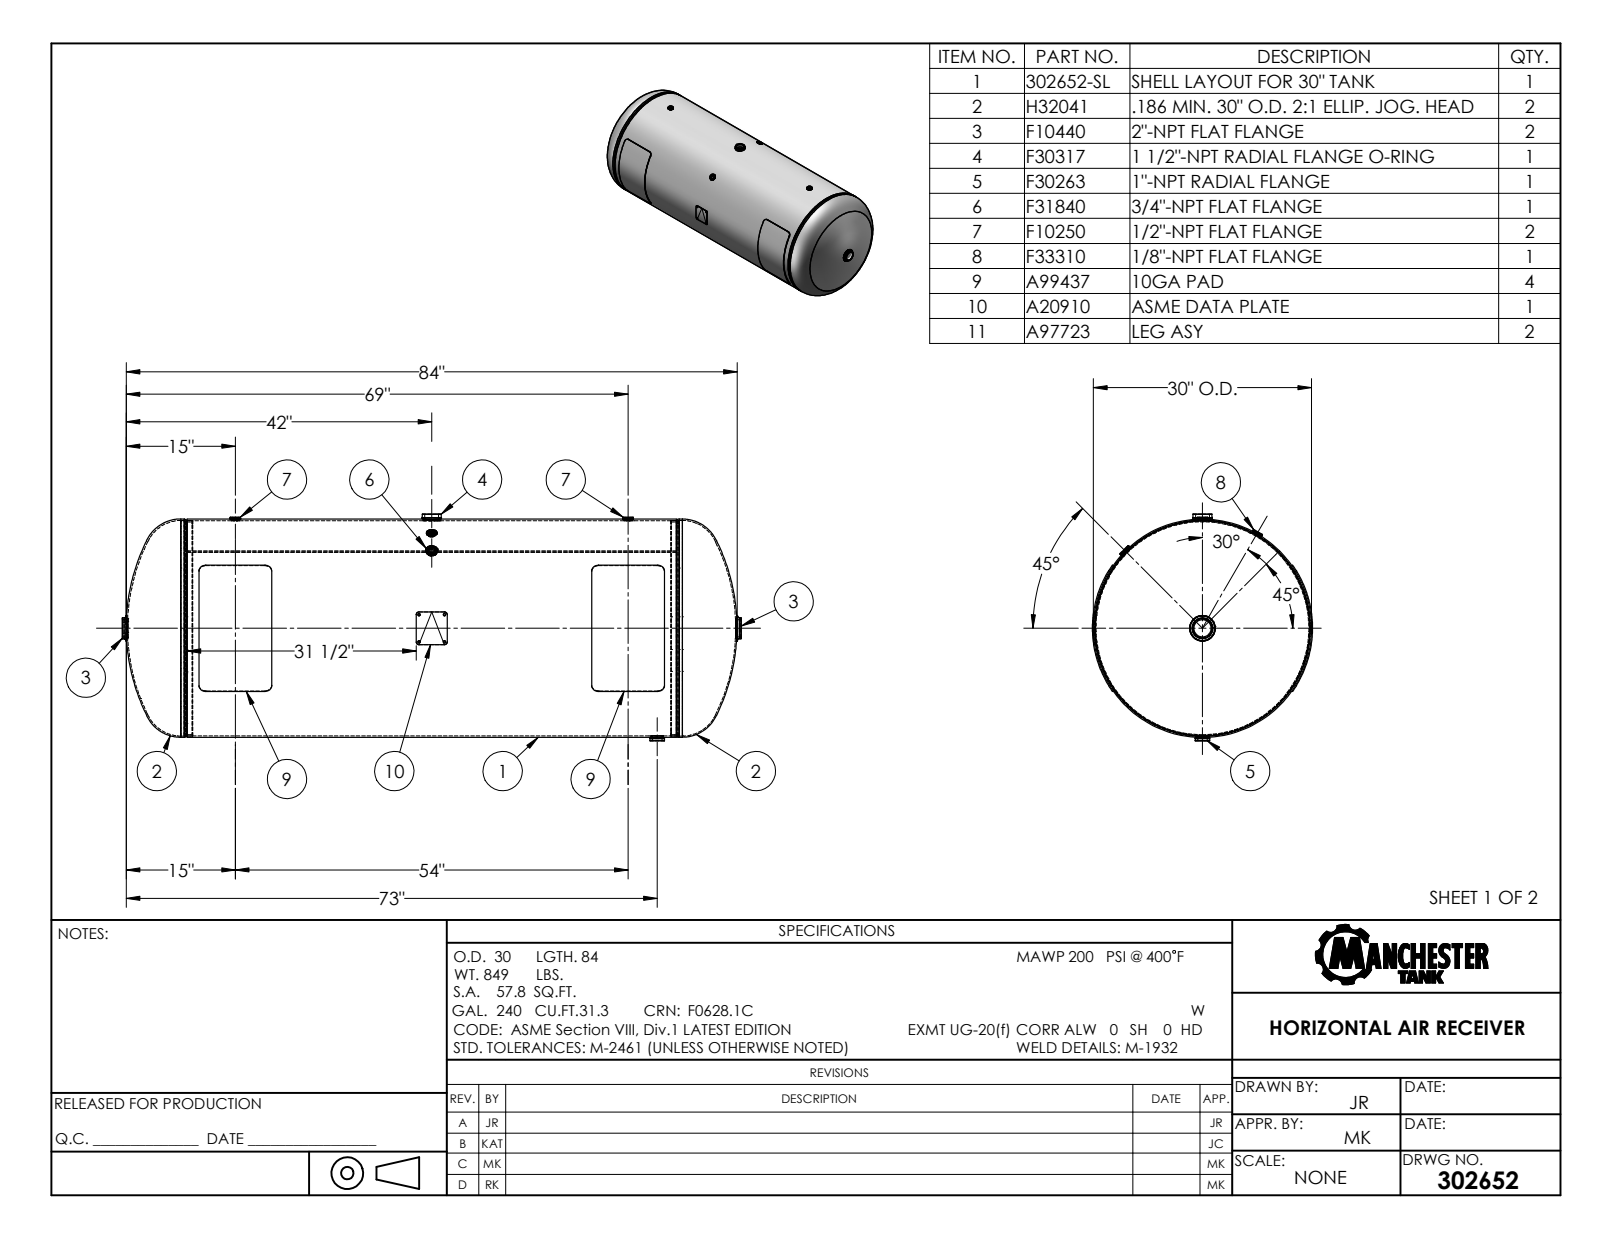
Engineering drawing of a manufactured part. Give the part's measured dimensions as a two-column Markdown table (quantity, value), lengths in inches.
| quantity | value |
| --- | --- |
| part name | 302652 |
| STEP written by | SolidWorks 2022 (AUTOMOTIVE_DESIGN) |
| units | inches |
| bodies | 30 solids, 592 faces (254 planar, 170 cylindrical, 168 other) |
| overall size | 85.138 × 42.5 × 34.974 |
| volume | 2 861 in³ |
| surface area | 27 420 in² |
| round holes (diameter × count) | 0.84 × 2, 0.405 × 1, 1.05 × 1, 1.315 × 1, 1.9 × 1, 2.375 × 1, 2.375 × 1, 29.256 × 1, 29.546 × 1, 29.628 × 1, 30 × 1 |
| round bosses / shafts (diameter × count) | 1.45 × 3, 1.438 × 3, 2.688 × 2, 1.062 × 2, 29.63 × 1, 3.5 × 1, 2.875 × 1, 2.266 × 1 |
| partial cylindrical surfaces (radius × count) | 0.125 × 16, 0.25 × 12, 0.281 × 8, 0.422 × 8, 0.474 × 4, 7 × 1, 7.5 × 1, 15.06 × 1 |
| main face-to-face distances | 0.172, 0.224, 35.828, 54, 8.828, 36, 9, 35.656, 8.656, 53.828 |
| hole center spacings | 27, 4, 31, 54, 58 |
